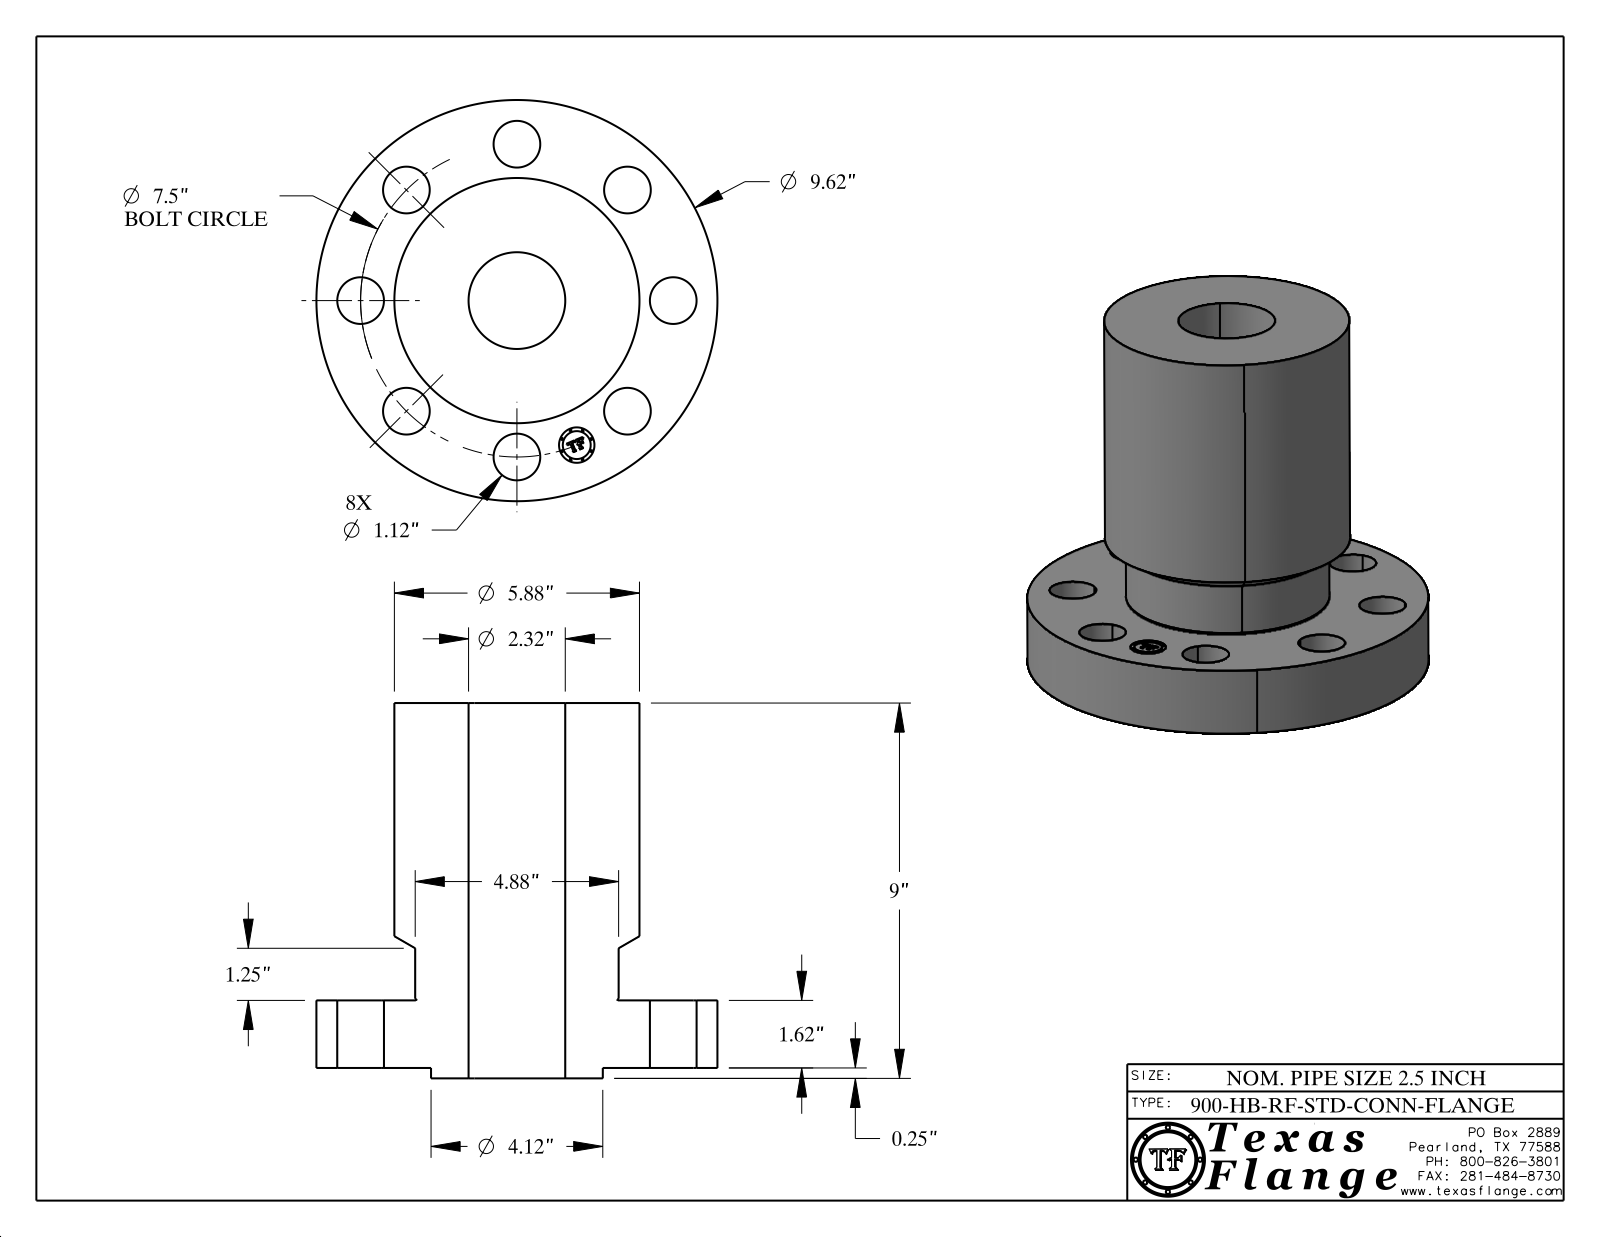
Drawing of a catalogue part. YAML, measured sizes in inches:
part_name: "2.5-900-HB-RF-STD-CONN-FLANGE"
step_written_by: "CATIA V5 STEP AP214 (AUTOMOTIVE_DESIGN)"
units: inches
bodies: {solids: 1, faces: 421, planar: 369, cylindrical: 46, other: 6}
overall_size: [9.62, 9.62, 9]
volume: 252
surface_area: 425.8
round_holes:
  - {diameter: 1.12, count: 8}
  - {diameter: 0.85, count: 1}
  - {diameter: 2.32, count: 1}
round_bosses_or_shafts:
  - {diameter: 0.051, count: 8}
  - {diameter: 9.62, count: 1}
  - {diameter: 5.88, count: 1}
  - {diameter: 4.88, count: 1}
  - {diameter: 4.12, count: 1}
  - {diameter: 0.67, count: 1}
face_to_face_distances: [1.62, 8.75, 7.13, 0.25, 1.87, 9, 1.865, 1.615, 7.135, 0.254]
hole_center_spacings: [3.75, 2.87, 5.303, 6.929, 1.463, 6.236, 7.356, 7.5]
